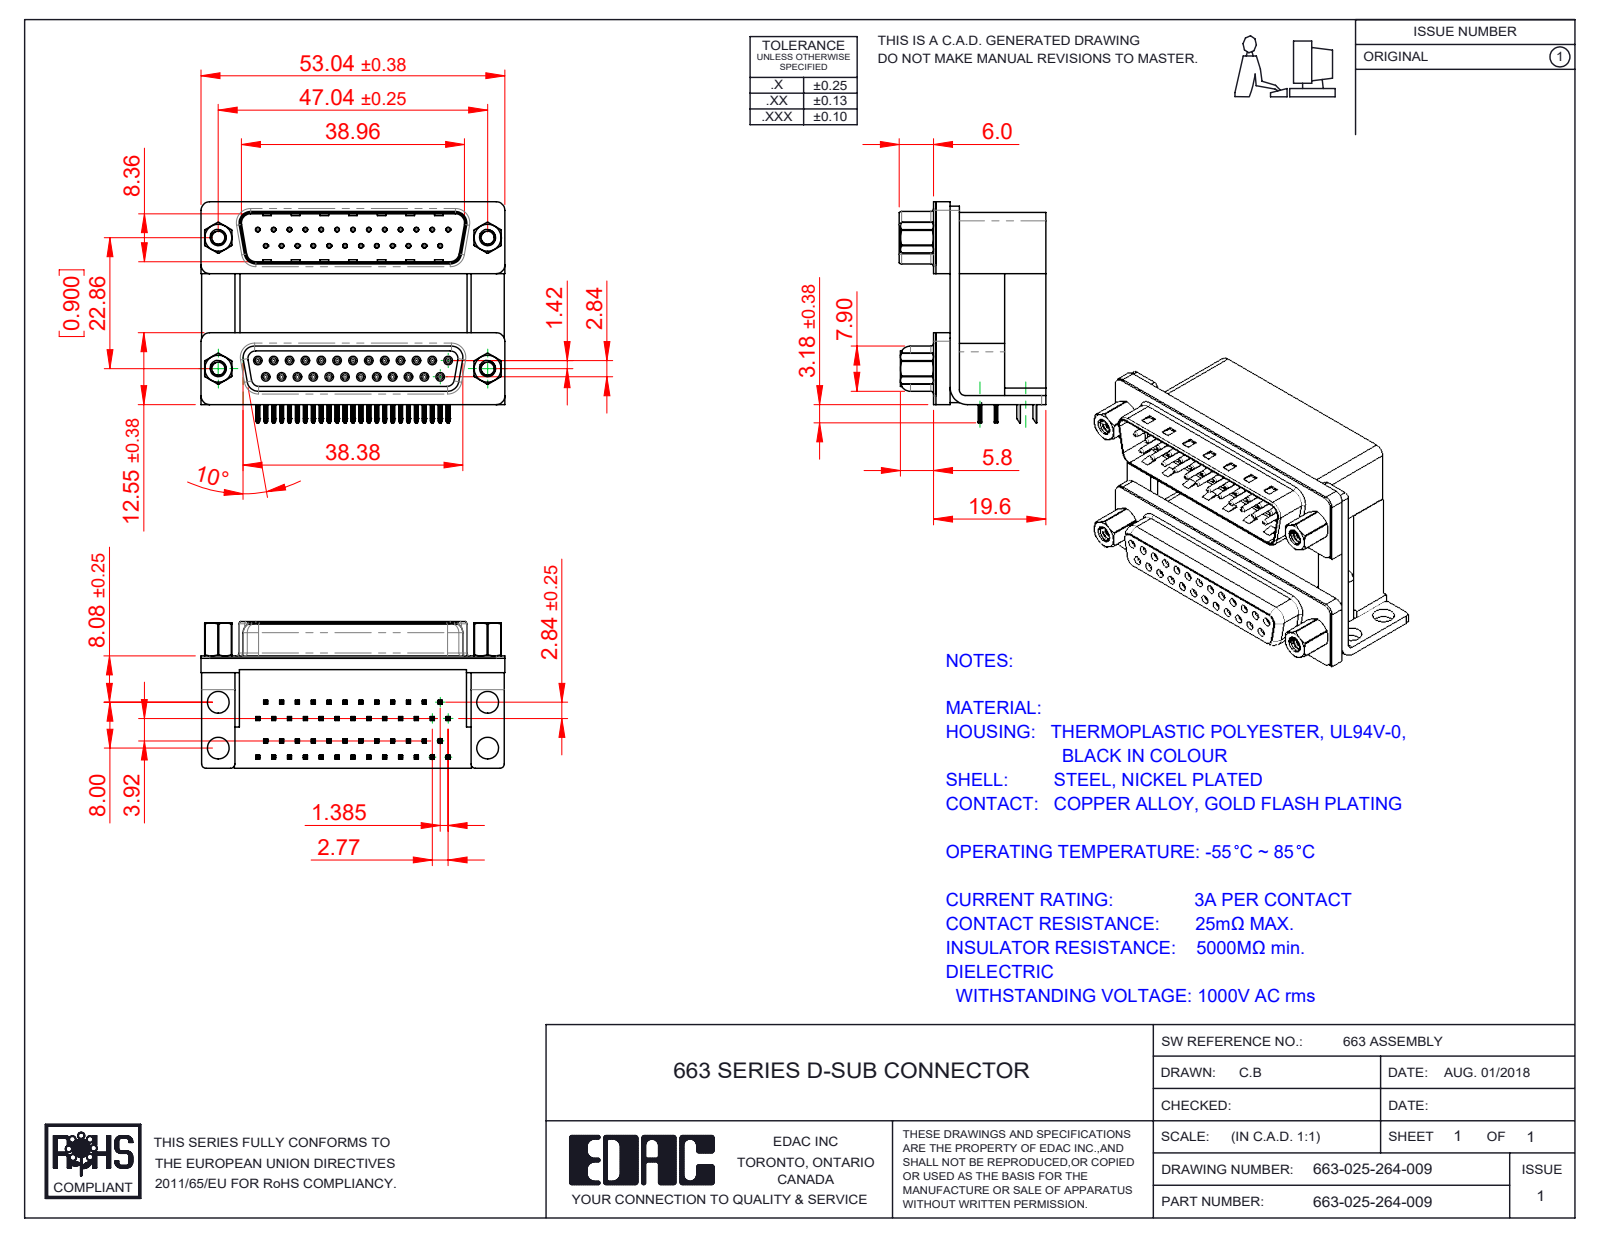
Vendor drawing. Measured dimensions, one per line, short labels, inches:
name: 663 Contact Bottom Upper_H; 663 Threaded Rivet_4-40; 663 Mounting Bracket_NoneH; 663 Shell Plug_25 Contacts (+8 more)
written by: SolidWorks 2020 (CONFIG_CONTROL_DESIGN)
unit: in
bodies: 65 solids, 6455 faces (3301 planar, 1687 cylindrical, 1467 other)
size: 2.088 × 1.519 × 1.008
volume: 1.472 in³; area: 40.07 in²
holes: 50× ⌀0.031, 25× ⌀0.014, 25× ⌀0.035, 4× ⌀0.089, 4× ⌀0.09, 4× ⌀0.138, 4× ⌀0.15, 4× ⌀0.157, 4× ⌀0.189, 4× ⌀0.197
bosses: 25× ⌀0.047, 25× ⌀0.03, 4× ⌀0.193, 4× ⌀0.187, 4× ⌀0.154, 4× ⌀0.11
rounds: 200× R0.004, 100× R0.006, 100× R0.01, 50× R0.005, 50× R0.014, 25× R0.013, 14× R0.059, 12× R0.011
face distances: 0.756, 0.472, 0.016, 0.283, 0.421, 0.657, 0.374, 0.098, 0.488, 0.9
hole spacings: 0.124, 0.109, 0.218, 0.436, 0.327, 0.198, 0.545, 0.294
